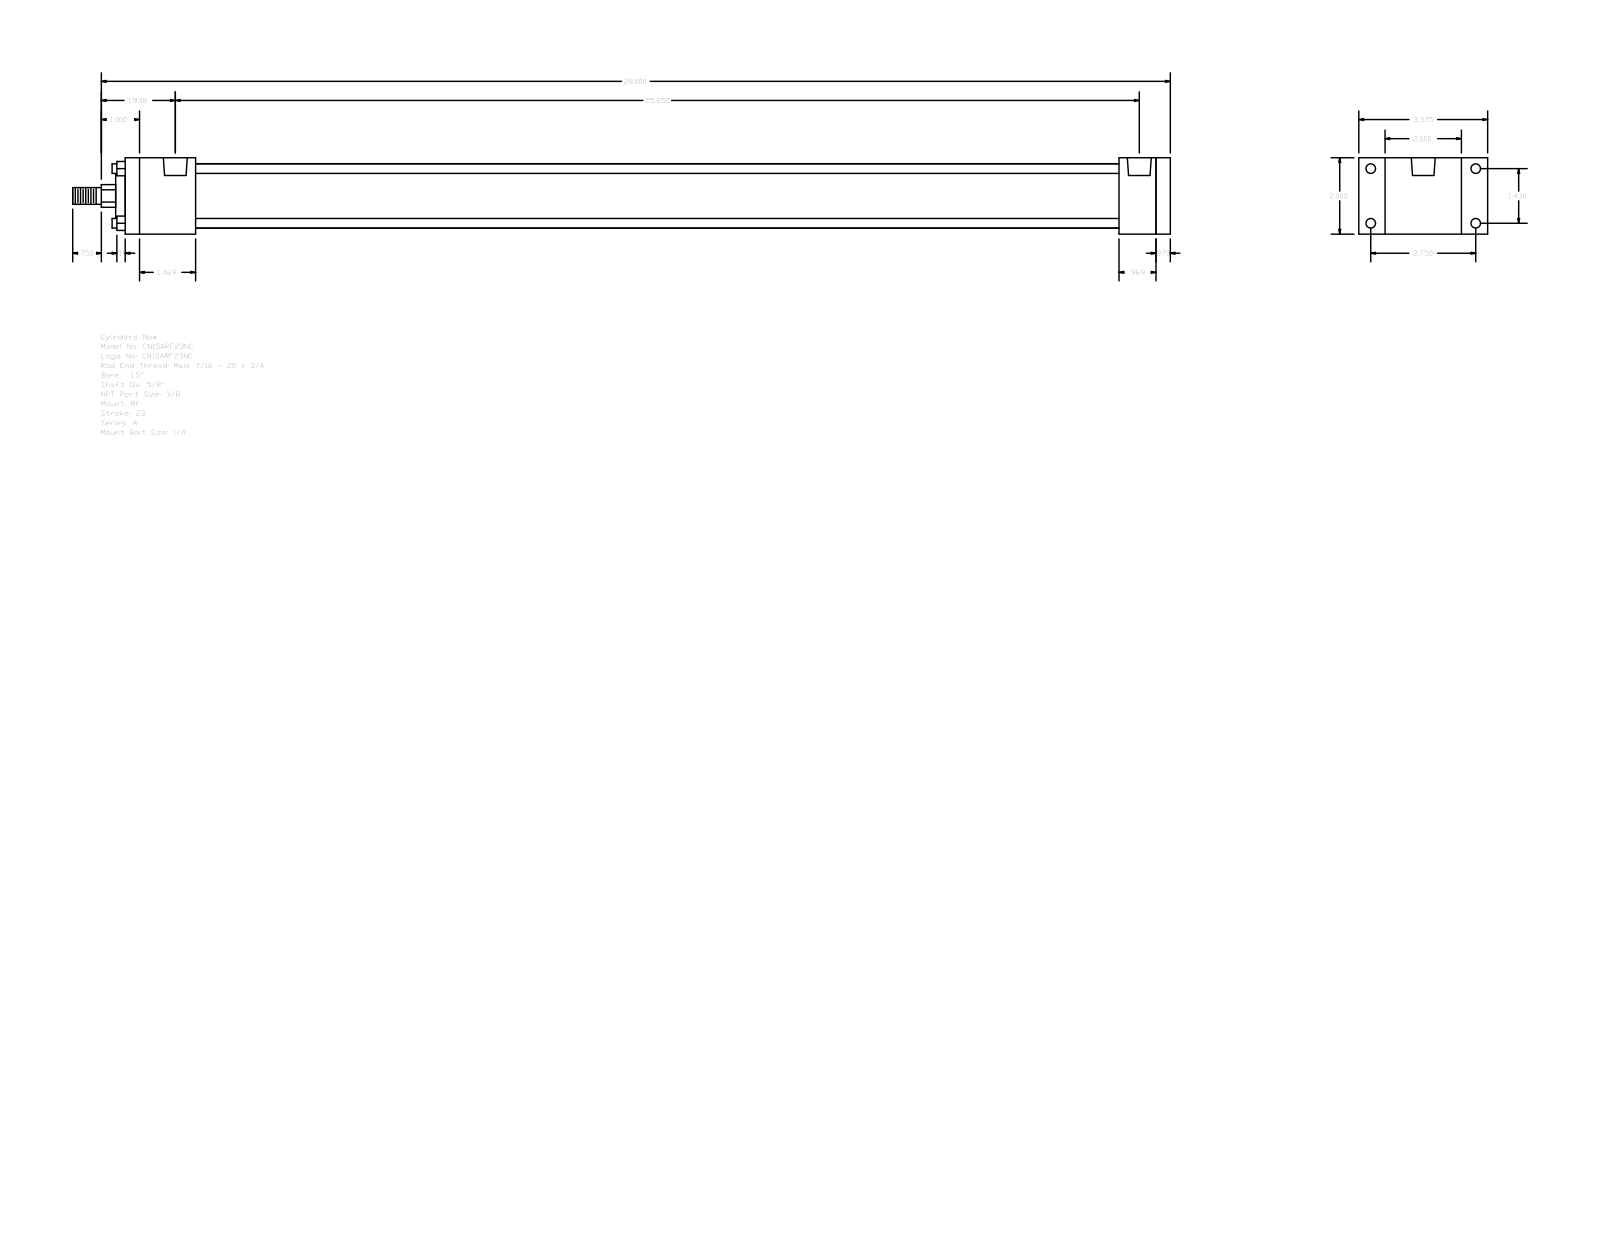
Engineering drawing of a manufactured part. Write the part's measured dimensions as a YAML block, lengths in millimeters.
part_name: "A_RF__0150_0.625"
step_written_by: "GSSL Pune (CONFIG_CONTROL_DESIGN)"
units: millimeters
bodies: {solids: 0, faces: 92, planar: 64, cylindrical: 28, other: 0}
overall_size: [730.25, 85.72, 50.8]
round_holes:
  - {diameter: 5.56, count: 4}
  - {diameter: 6.35, count: 4}
  - {diameter: 15.93, count: 2}
round_bosses_or_shafts:
  - {diameter: 6.35, count: 4}
  - {diameter: 42.93, count: 1}
  - {diameter: 28.57, count: 1}
  - {diameter: 15.88, count: 1}
  - {diameter: 11.11, count: 1}
partial_cylinders:
  - {radius: 7.54, count: 1}
face_to_face_distances: [50.8, 9.53, 695.32, 685.79, 661.19, 24.6, 34.13, 46.83, 614.36, 638.96]
hole_center_spacings: [3.97, 36.32, 69.84, 78.72, 633.41, 637.38, 641.35]
